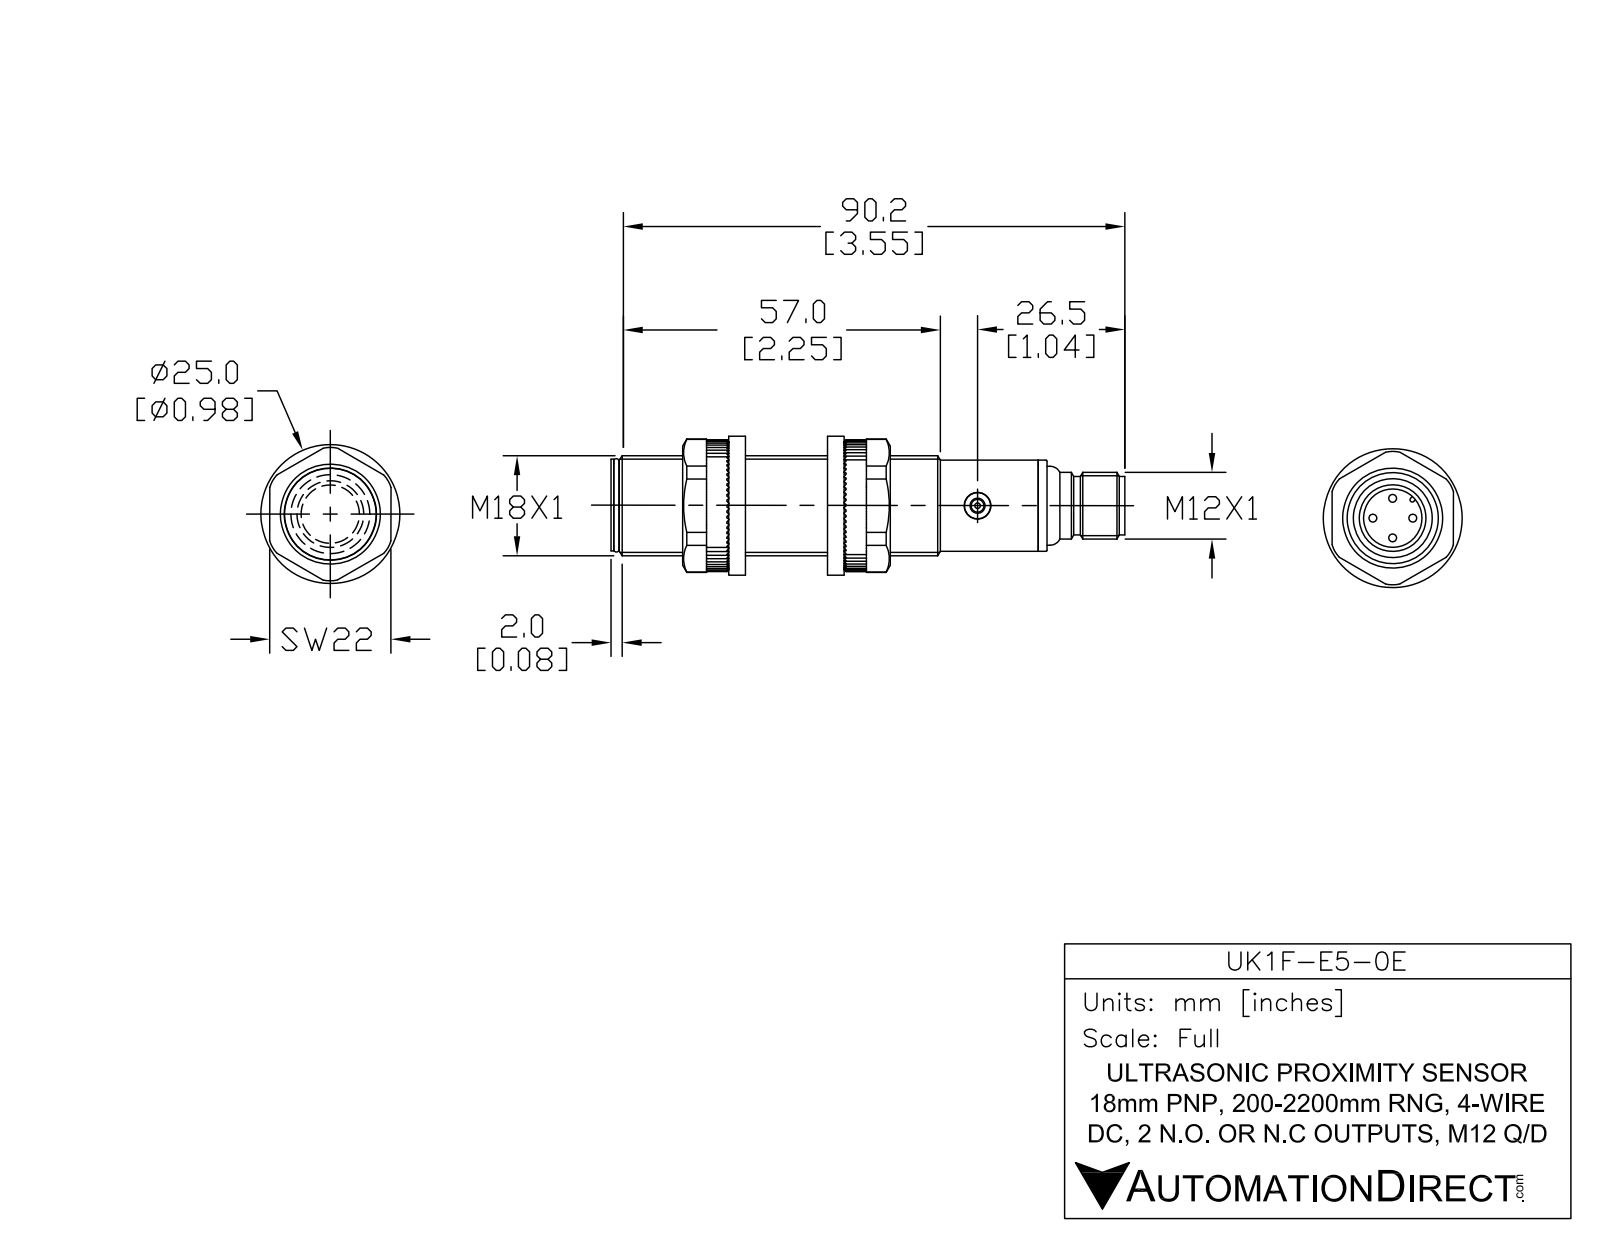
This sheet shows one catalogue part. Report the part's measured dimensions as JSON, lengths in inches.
{"part_name": "UK1F-E5-0E", "step_written_by": "SolidWorks 2017 (AUTOMOTIVE_DESIGN)", "units": "inches", "bodies": {"solids": 6, "faces": 106, "planar": 21, "cylindrical": 48, "other": 37}, "overall_size": [3.606, 0.709, 0.709], "volume_in3": 1.202, "surface_area_in2": 10.68, "round_holes": [[0.106, 1], [0.185, 1], [0.276, 1], [0.327, 1], [0.374, 1]], "round_bosses_or_shafts": [[0.039, 4], [0.709, 1], [0.654, 1], [0.646, 1], [0.622, 1], [0.559, 1], [0.472, 1], [0.413, 1]], "partial_cylinders_radius": [[0.024, 1]], "face_to_face_distances": [2.957, 0.039, 2.996, 0.037, 2.994, 0.043, 0.157, 3.055, 3.053, 3.016]}
